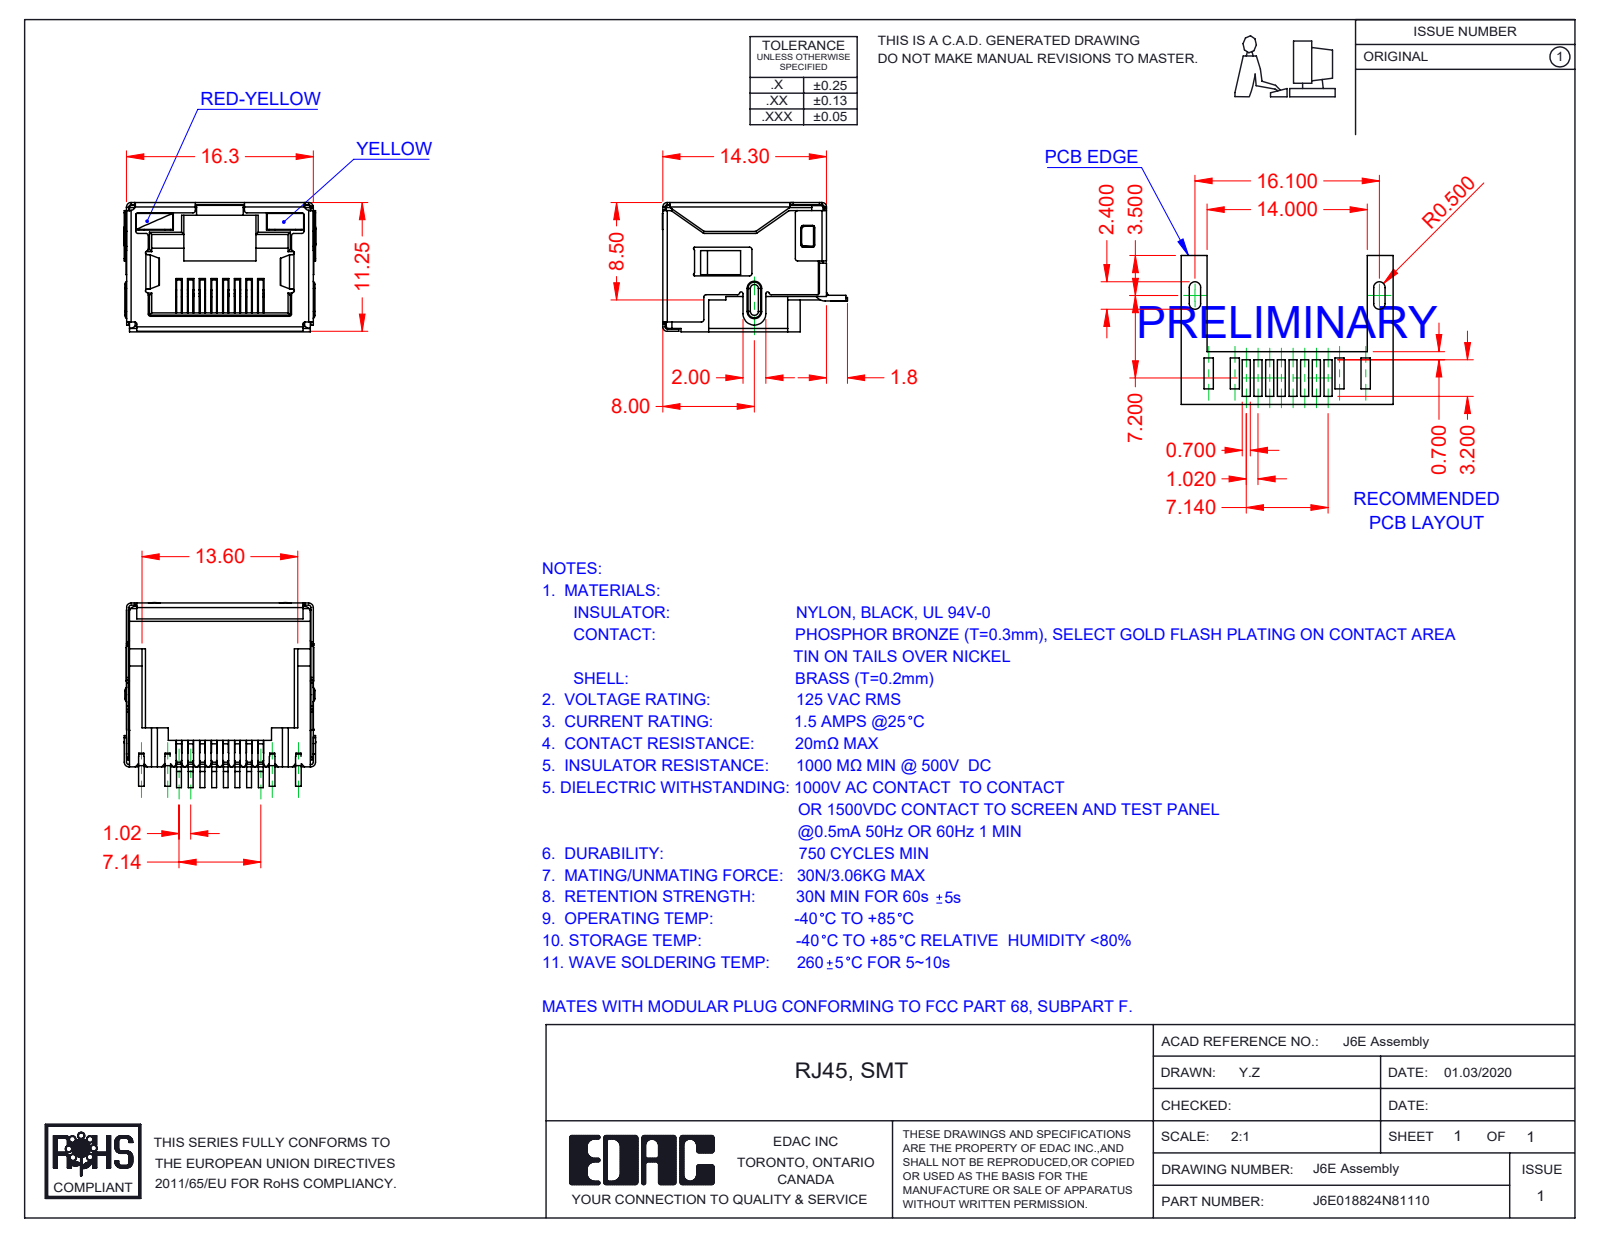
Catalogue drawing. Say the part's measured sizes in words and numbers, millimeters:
The part is named "6E LED RH_1-Yellow; J6E018824N81110; 6E LED LH_8-Red-Yellow; 6E Shield_LED (+2 more)". Its 3-D file was written by "SolidWorks 2016 (CONFIG_CONTROL_DESIGN)". It is 12 solids with 1498 faces: 1099 planar, 349 cylindrical and 50 other. Overall it measures 16.75 by 16.15 by 11.3 millimeters. Its volume is 1 109 cubic millimeters and its surface area 4 045 square millimeters. Partial cylindrical surfaces (rounded edges, fillets, slot ends): 82 of radius 0.2, 17 of radius 0.25, 13 of radius 0.4, 13 of radius 0.5, 10 of radius 0.1, 7 of radius 0.15, 4 of radius 0.3, 3 of radius 1. The main face-to-face distances are 11.05, 16.05, 16.1, 15.85, 11.1, 11.3, 2.4, 0.7, 9.85, 0.49.
